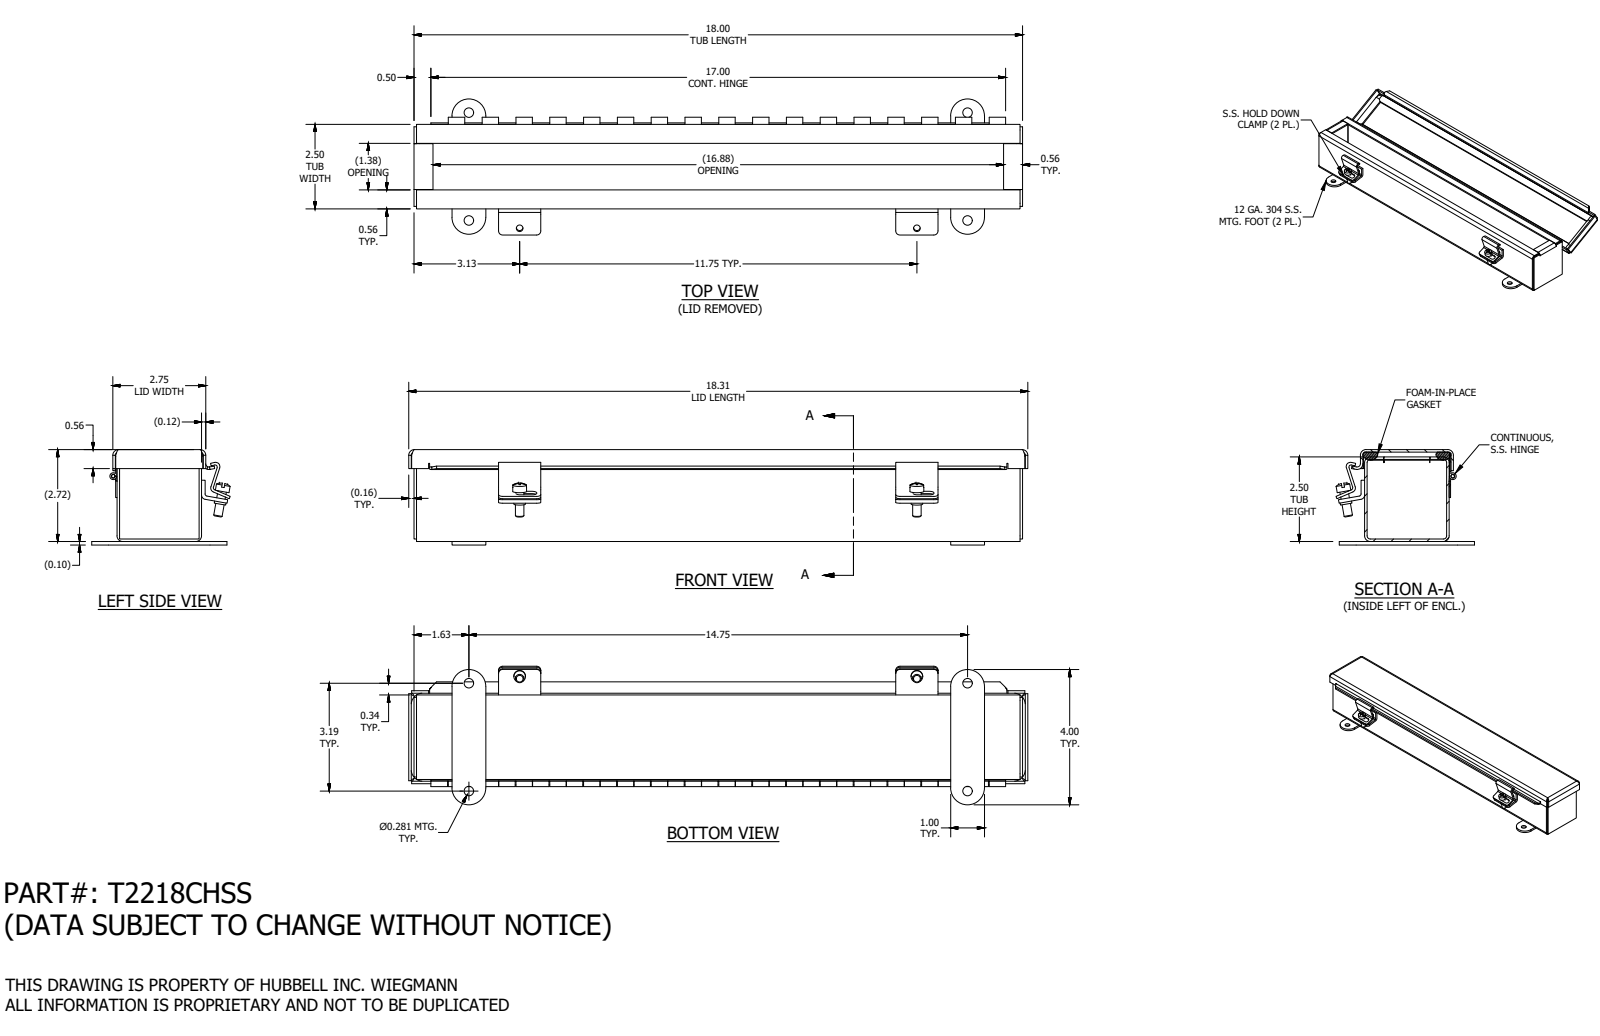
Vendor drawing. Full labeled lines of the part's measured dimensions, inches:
Part name (STEP PRODUCT): T2218CHSS
STEP written by: SolidWorks 2019 (AUTOMOTIVE_DESIGN)
Units: inches
Bodies: 16 solids, 466 faces (281 planar, 153 cylindrical, 32 other)
Overall size (bounding box): 18.313 × 4.098 × 2.822
Volume: 23.16 in³ · Surface area: 611.1 in²
Round holes (diameter × count): ⌀0.11 ×4, ⌀0.281 ×4, ⌀0.196 ×2, ⌀0.116 ×1
Round bosses / shafts (diameter × count): ⌀0.41 ×2, ⌀0.344 ×2, ⌀0.25 ×2, ⌀0.2 ×1, ⌀0.1 ×1
Partial cylindrical surfaces — rounded edges, fillets, slot ends (radius × count): R0.094 ×11, R0.168 ×11, R0.085 ×8, R0.125 ×8, R0.133 ×4, R0.242 ×4, R0.5 ×4, R0.063 ×3
Main face-to-face distances: 0.074, 2.426, 2.644, 2.5, 2.352, 2.718, 2.57, 0.218, 2.552, 0.126
Hole centre spacings: 0.75, 3.187, 11.75, 14.75, 15.09, 11, 11.75, 12.5
